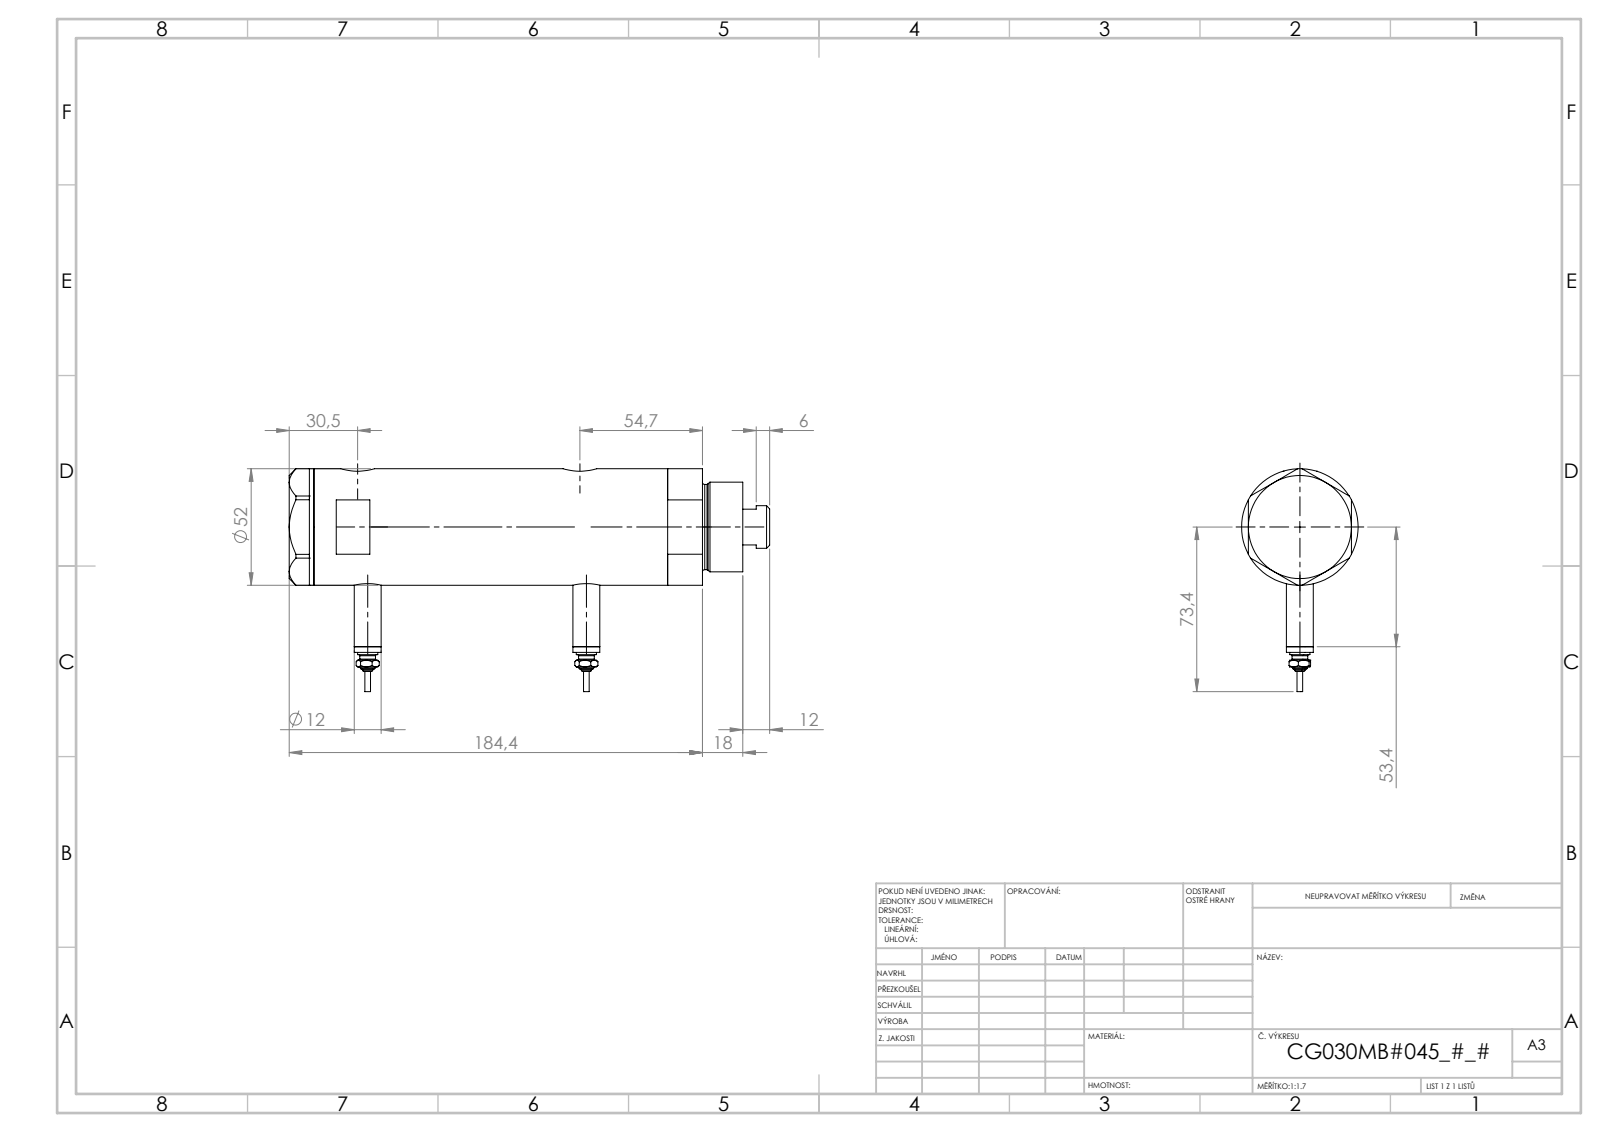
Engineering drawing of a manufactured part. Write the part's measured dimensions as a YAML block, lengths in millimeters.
part_name: "Switch; V270CG_BACK; V270CG_MIDDLE; V270CG_VC (+1 more)"
step_written_by: "SolidWorks 2019 (CONFIG_CONTROL_DESIGN)"
units: millimeters
bodies: {solids: 6, faces: 226, planar: 93, cylindrical: 69, other: 64}
overall_size: [214.4, 99.4, 52]
volume: 398755
surface_area: 89998
round_holes:
  - {diameter: 9.73, count: 2}
  - {diameter: 12.5, count: 2}
  - {diameter: 15, count: 2}
  - {diameter: 6.5, count: 1}
  - {diameter: 20, count: 1}
  - {diameter: 21.5, count: 1}
  - {diameter: 30, count: 1}
  - {diameter: 33, count: 1}
  - {diameter: 44, count: 1}
round_bosses_or_shafts:
  - {diameter: 12, count: 2}
  - {diameter: 9, count: 2}
  - {diameter: 7, count: 2}
  - {diameter: 4.5, count: 2}
  - {diameter: 2.5, count: 2}
  - {diameter: 52, count: 1}
  - {diameter: 40, count: 1}
  - {diameter: 38, count: 1}
face_to_face_distances: [121.5, 23.8, 97.7, 11, 34.8, 132.5, 46, 36.4, 168.9, 157.9]
hole_center_spacings: [2.9, 4.5, 94.7, 97.6, 99.2, 102.1]
